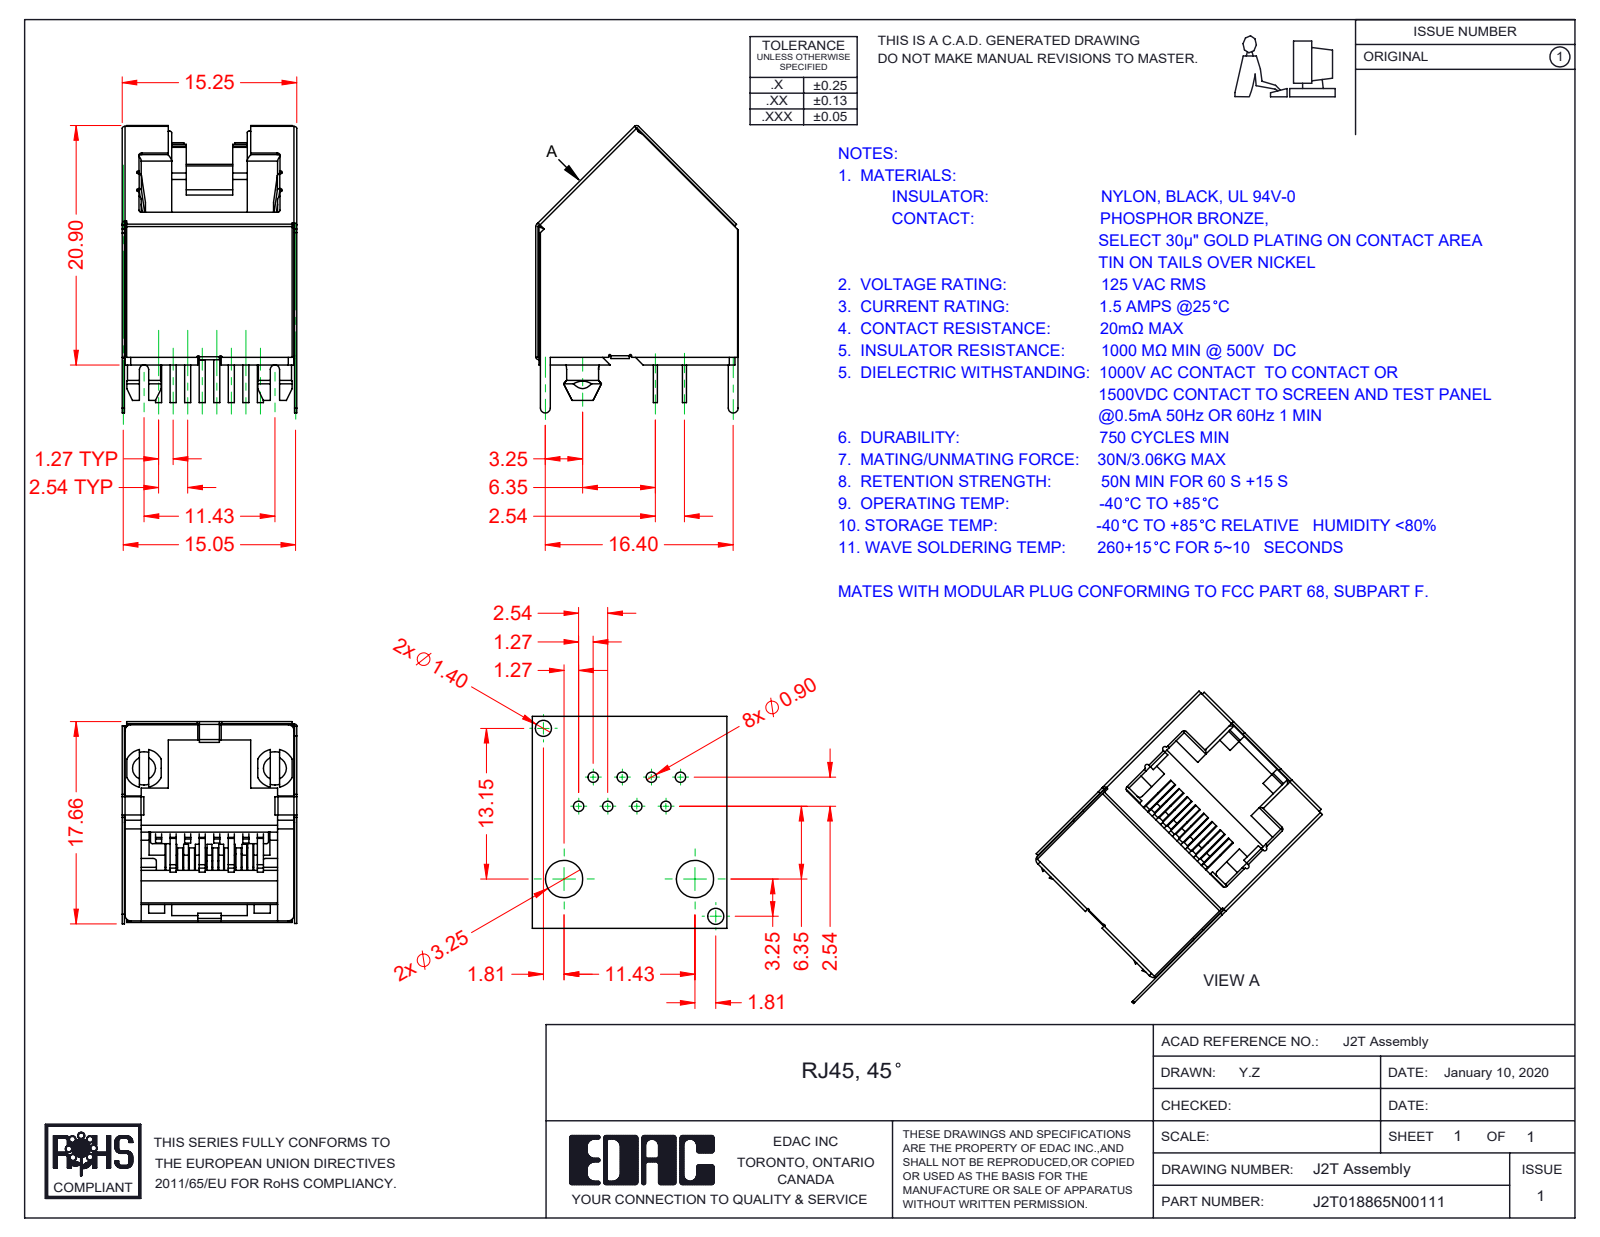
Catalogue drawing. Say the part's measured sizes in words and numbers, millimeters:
The part is named "2T Insulator; 2T Contact Lock; 2T Shell; RJ2T018865N00111 (+1 more)". Its 3-D file was written by "SolidWorks 2016 (CONFIG_CONTROL_DESIGN)". It is 11 solids with 631 faces: 447 planar, 161 cylindrical and 23 other. Overall it measures 25.09 by 17.66 by 15.25 millimeters. Its volume is 1 960 cubic millimeters and its surface area 5 178 square millimeters. Round bosses or shafts: 2 of diameter 2.9. Partial cylindrical surfaces (rounded edges, fillets, slot ends): 21 of radius 0.5, 16 of radius 1, 12 of radius 0.2, 10 of radius 0.25, 8 of radius 1.46, 8 of radius 1.52, 5 of radius 0.1, 3 of radius 0.3. The main face-to-face distances are 15.04, 1.42, 13.33, 14.8, 15, 15.24, 14.84, 14.99, 14.79, 14.75.
